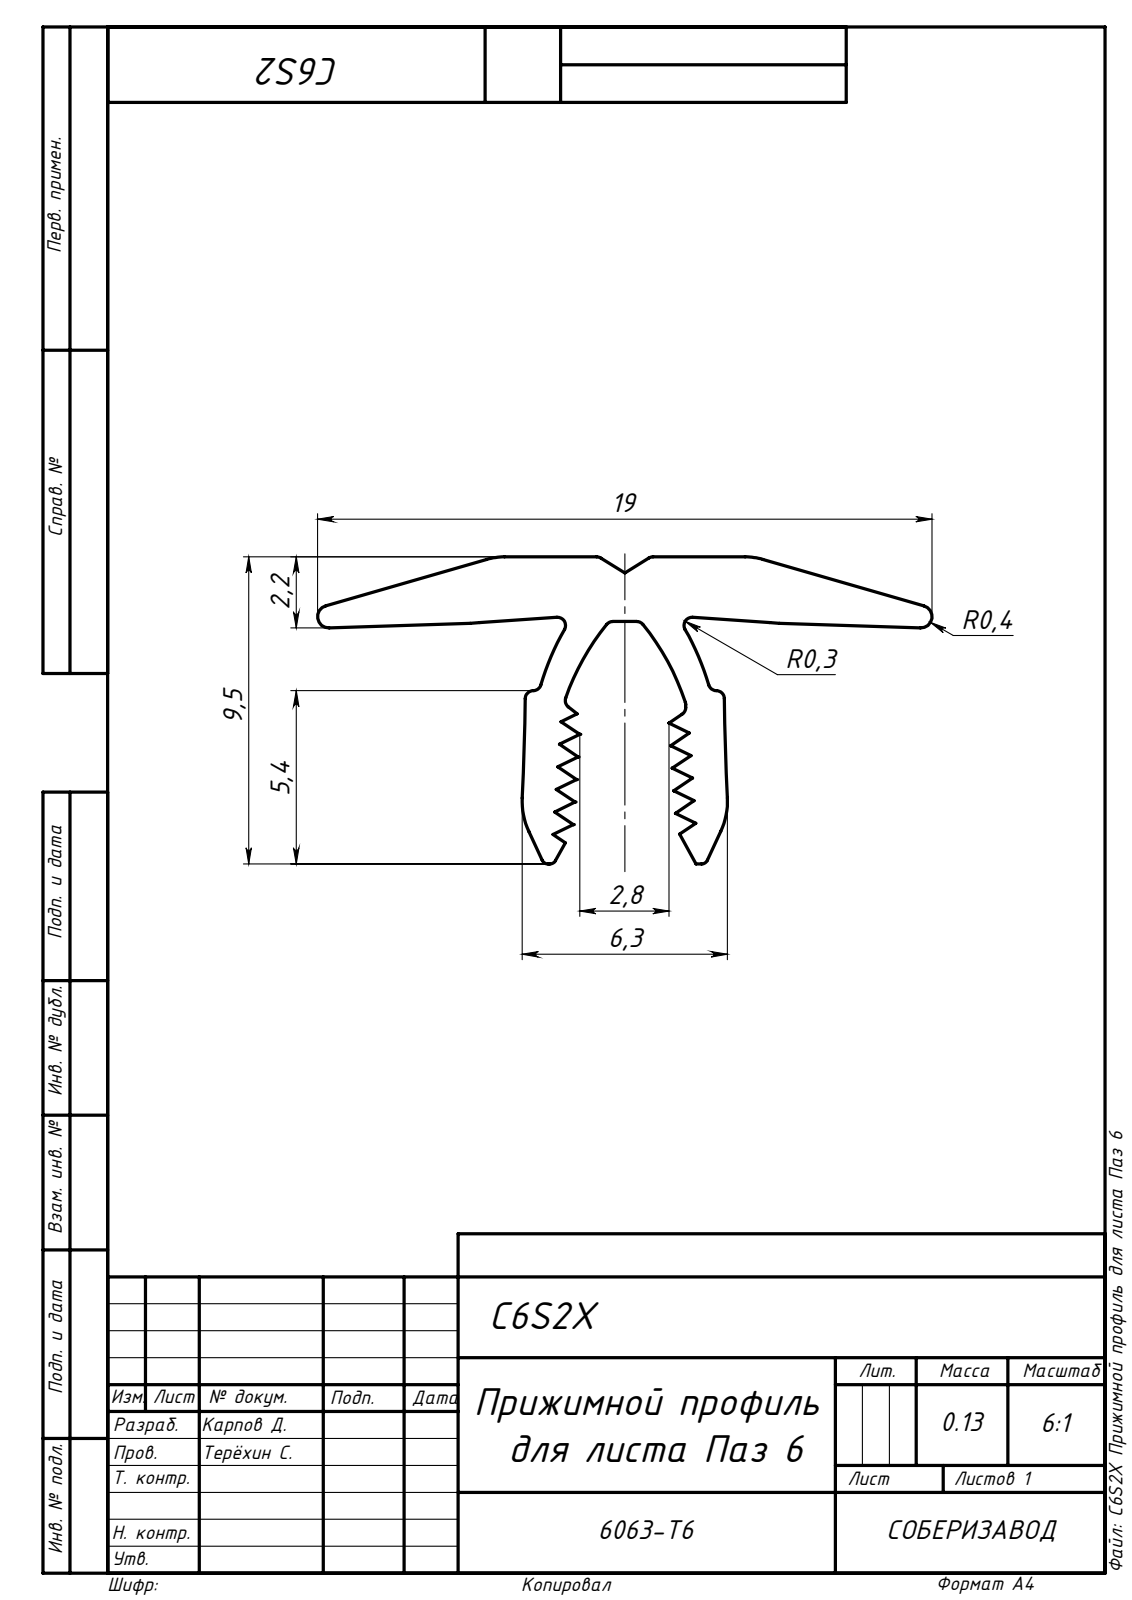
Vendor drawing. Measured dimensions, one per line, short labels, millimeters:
name: C6S2X Прижимной профиль для листа Паз 6
written by: SolidWorks 2019 (AUTOMOTIVE_DESIGN)
unit: mm
bodies: 1 solid, 95 faces (63 planar, 32 cylindrical, 0 other)
size: 120.02 × 19 × 9.5
volume: 5 691 mm³; area: 9 380 mm²
rounds: 13× R0.25, 3× R0.2, 2× R0.35, 2× R2, 2× R2.2, 2× R4, 2× R7.61, 2× R8.23
face distances: 1.21, 0.61, 0.6, 1.82, 2.42, 1.81, 3.03, 1.22, 2.43, 2
